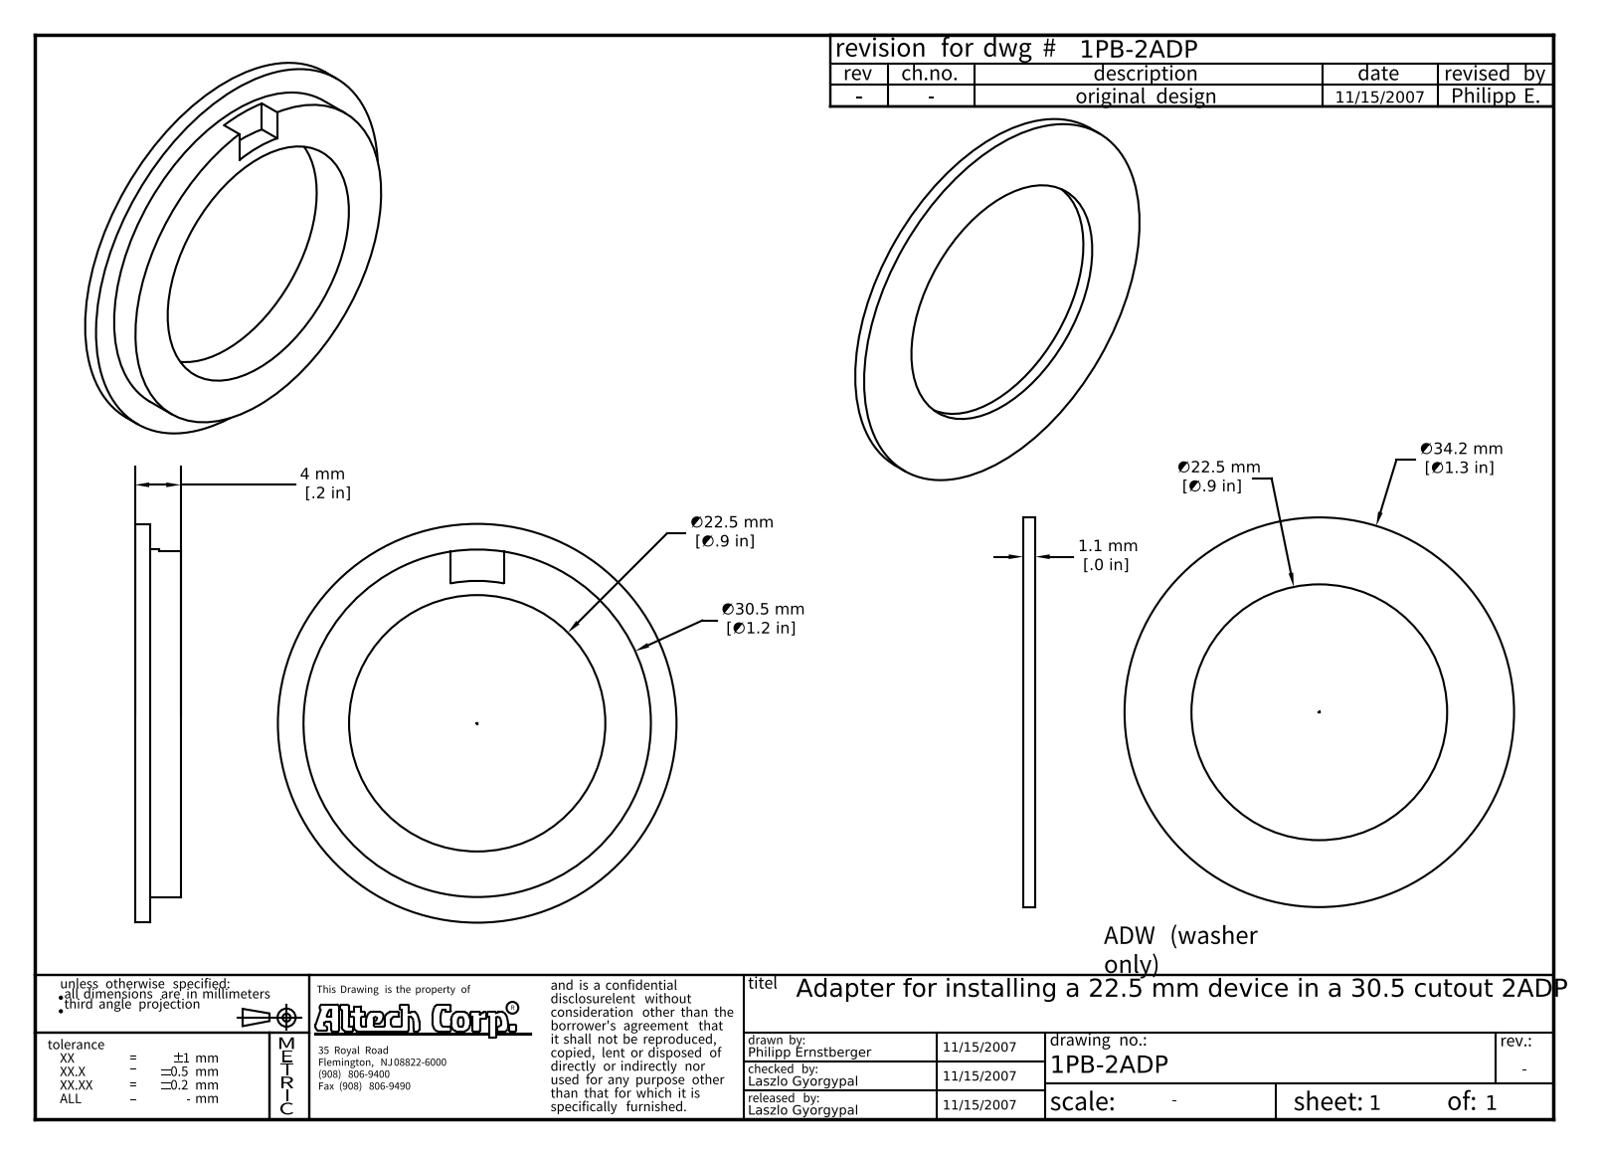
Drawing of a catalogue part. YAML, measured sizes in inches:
part_name: "2ADP"
step_written_by: "Autodesk Inventor 2008 (AUTOMOTIVE_DESIGN)"
units: inches
bodies: {solids: 1, faces: 10, planar: 6, cylindrical: 4, other: 0}
overall_size: [1.378, 1.378, 0.157]
volume: 0.099
surface_area: 2.829
round_holes:
  - {diameter: 0.886, count: 1}
round_bosses_or_shafts:
  - {diameter: 1.378, count: 1}
  - {diameter: 1.201, count: 1}
partial_cylinders:
  - {radius: 0.492, count: 1}
face_to_face_distances: [0.157, 0.053, 0.104, 0.083, 0.03, 0.075, 0.185]
